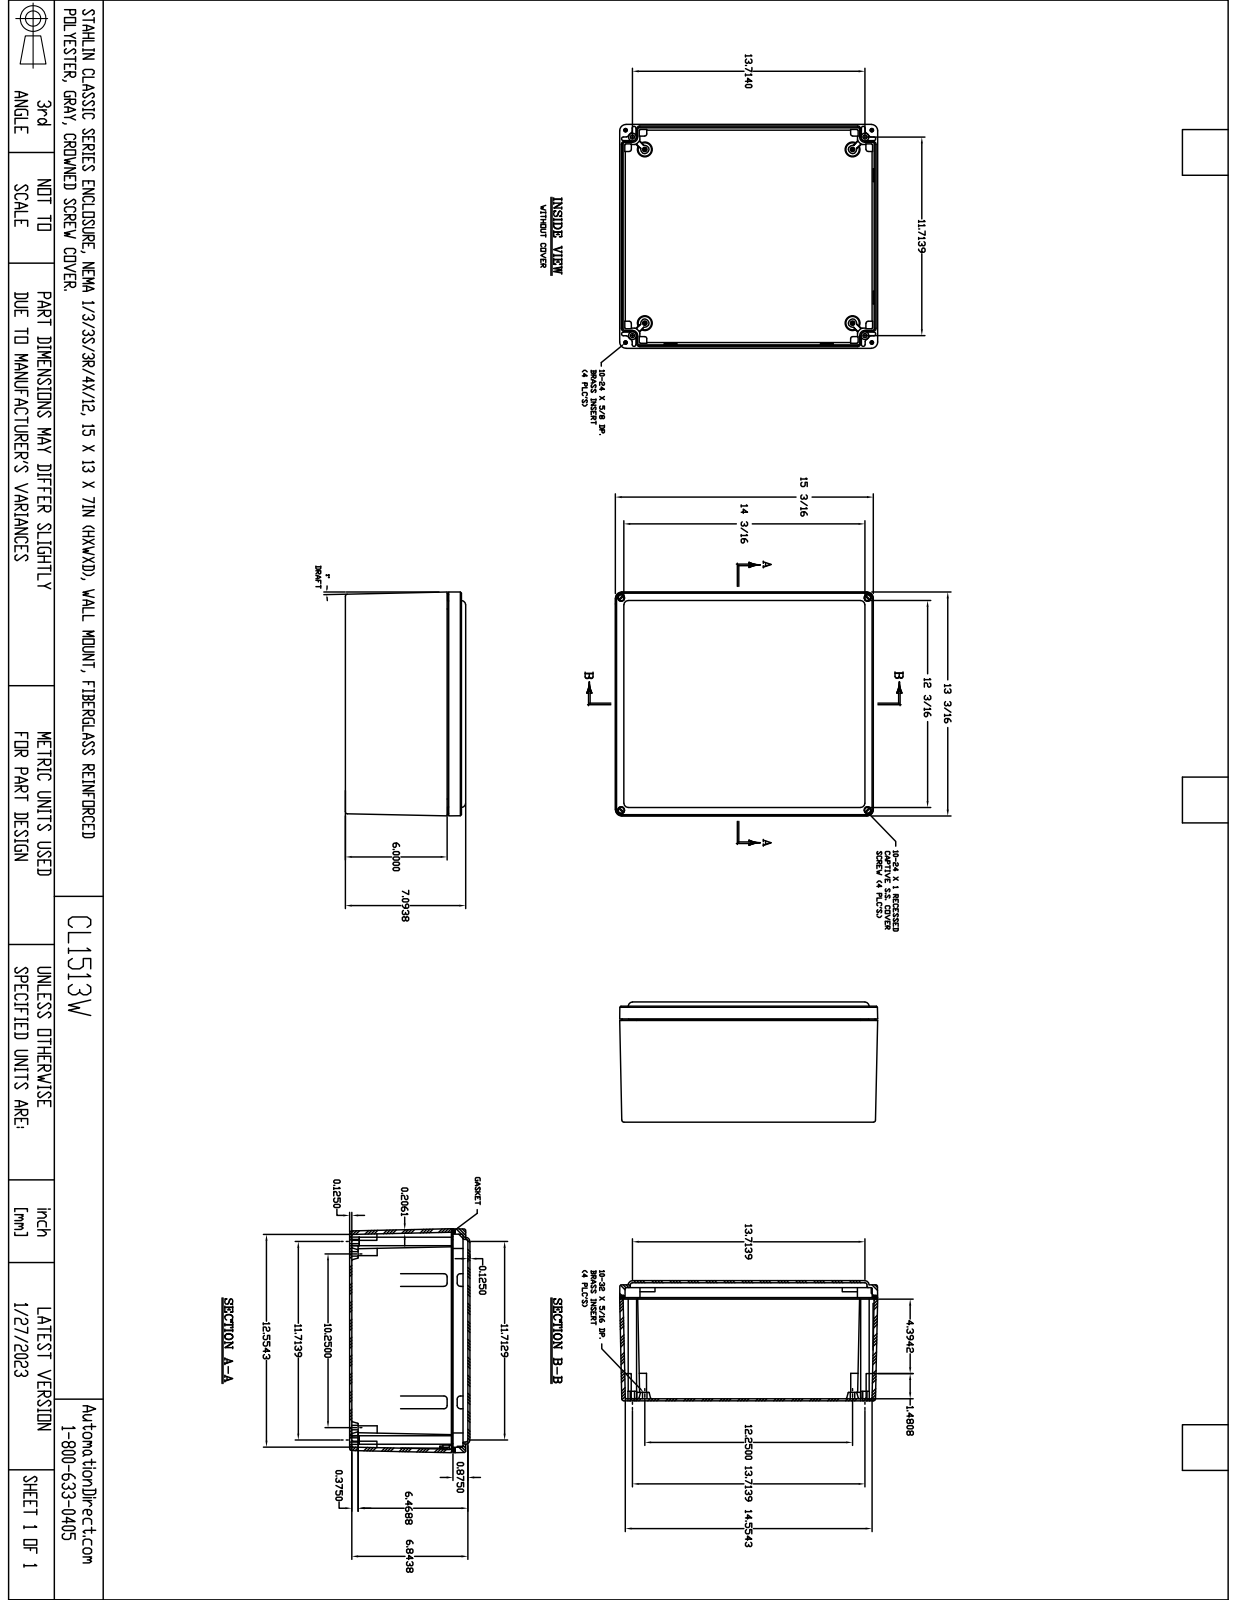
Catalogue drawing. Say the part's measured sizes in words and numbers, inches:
The part is named "CE1513W". Its 3-D file was written by "SolidWorks 2018 (AUTOMOTIVE_DESIGN)". It is 24 solids with 1127 faces: 453 planar, 306 cylindrical and 368 other. Overall it measures 15.22 by 13.22 by 7.094 inches. Its volume is 138.9 cubic inches and its surface area 1 675 square inches. Round holes: 8 of diameter 0.281, 4 of diameter 0.156, 4 of diameter 0.156, 4 of diameter 0.19, 4 of diameter 0.219, 4 of diameter 0.23, 4 of diameter 0.28, 4 of diameter 0.313, 4 of diameter 0.406, 4 of diameter 0.531, 3 of diameter 0.145, 1 of diameter 0.145. Round bosses or shafts: 4 of diameter 0.375, 4 of diameter 0.364, 4 of diameter 0.191. Partial cylindrical surfaces (rounded edges, fillets, slot ends): 57 of radius 0.031, 40 of radius 0.125, 23 of radius 0.062, 16 of radius 0.01, 8 of radius 0.059, 8 of radius 0.063, 8 of radius 0.188, 8 of radius 0.188. The main face-to-face distances are 0.186, 0.125, 6.844, 7.094, 6.969, 0.125, 6.969, 0.25, 6.719, 0.75. The hole center spacings are 0.574, 0.574, 1.039, 1.613, 1.613, 11.01, 11.448, 11.449.
